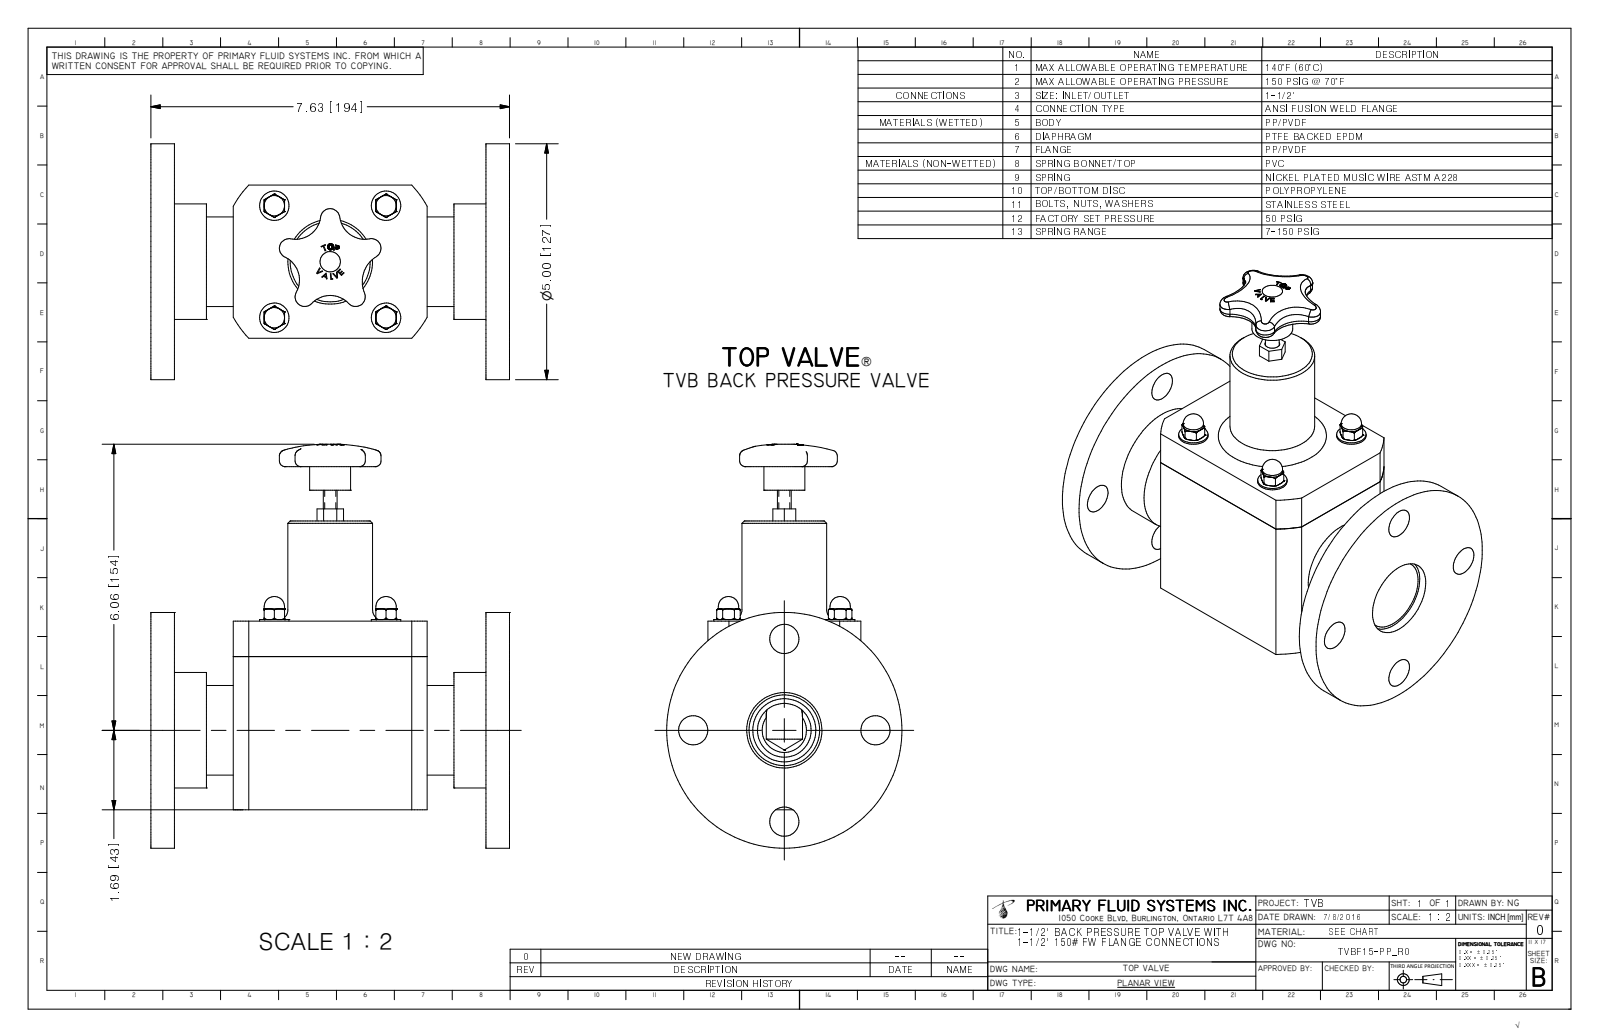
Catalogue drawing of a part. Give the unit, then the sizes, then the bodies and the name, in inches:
Units: inches
Overall size (bounding box): 8.565 × 7.625 × 5
Round holes (diameter × count): ⌀0.175 ×4, ⌀0.62 ×4, ⌀0.281 ×1, ⌀1.5 ×1, ⌀1.6 ×1
Round bosses / shafts (diameter × count): ⌀0.625 ×4, ⌀0.433 ×4, ⌀0.375 ×4, ⌀5 ×1, ⌀2.45 ×1, ⌀1.9 ×1, ⌀1.8 ×1, ⌀0.87 ×1
Partial cylindrical surfaces — rounded edges, fillets, slot ends (radius × count): R0.085 ×5, R0.205 ×5, R0.536 ×4, R0.656 ×4, R0.625 ×1, R0.745 ×1, R2.375 ×1
Main face-to-face distances: 0.5, 7.125, 7.625, 3.25, 6.625, 1.75, 5.875, 1.25, 5.375, 4
Hole centre spacings: 1.937, 2.74, 2.375, 2.375, 3.359, 3.875
Volume: 77.85 in³ · Surface area: 244.7 in²
Bodies: 1 solid, 372 faces (155 planar, 64 cylindrical, 153 other)
Part name (STEP PRODUCT): TVBF15-PP_R0
STEP written by: Autodesk Inventor 2009 (AUTOMOTIVE_DESIGN)
